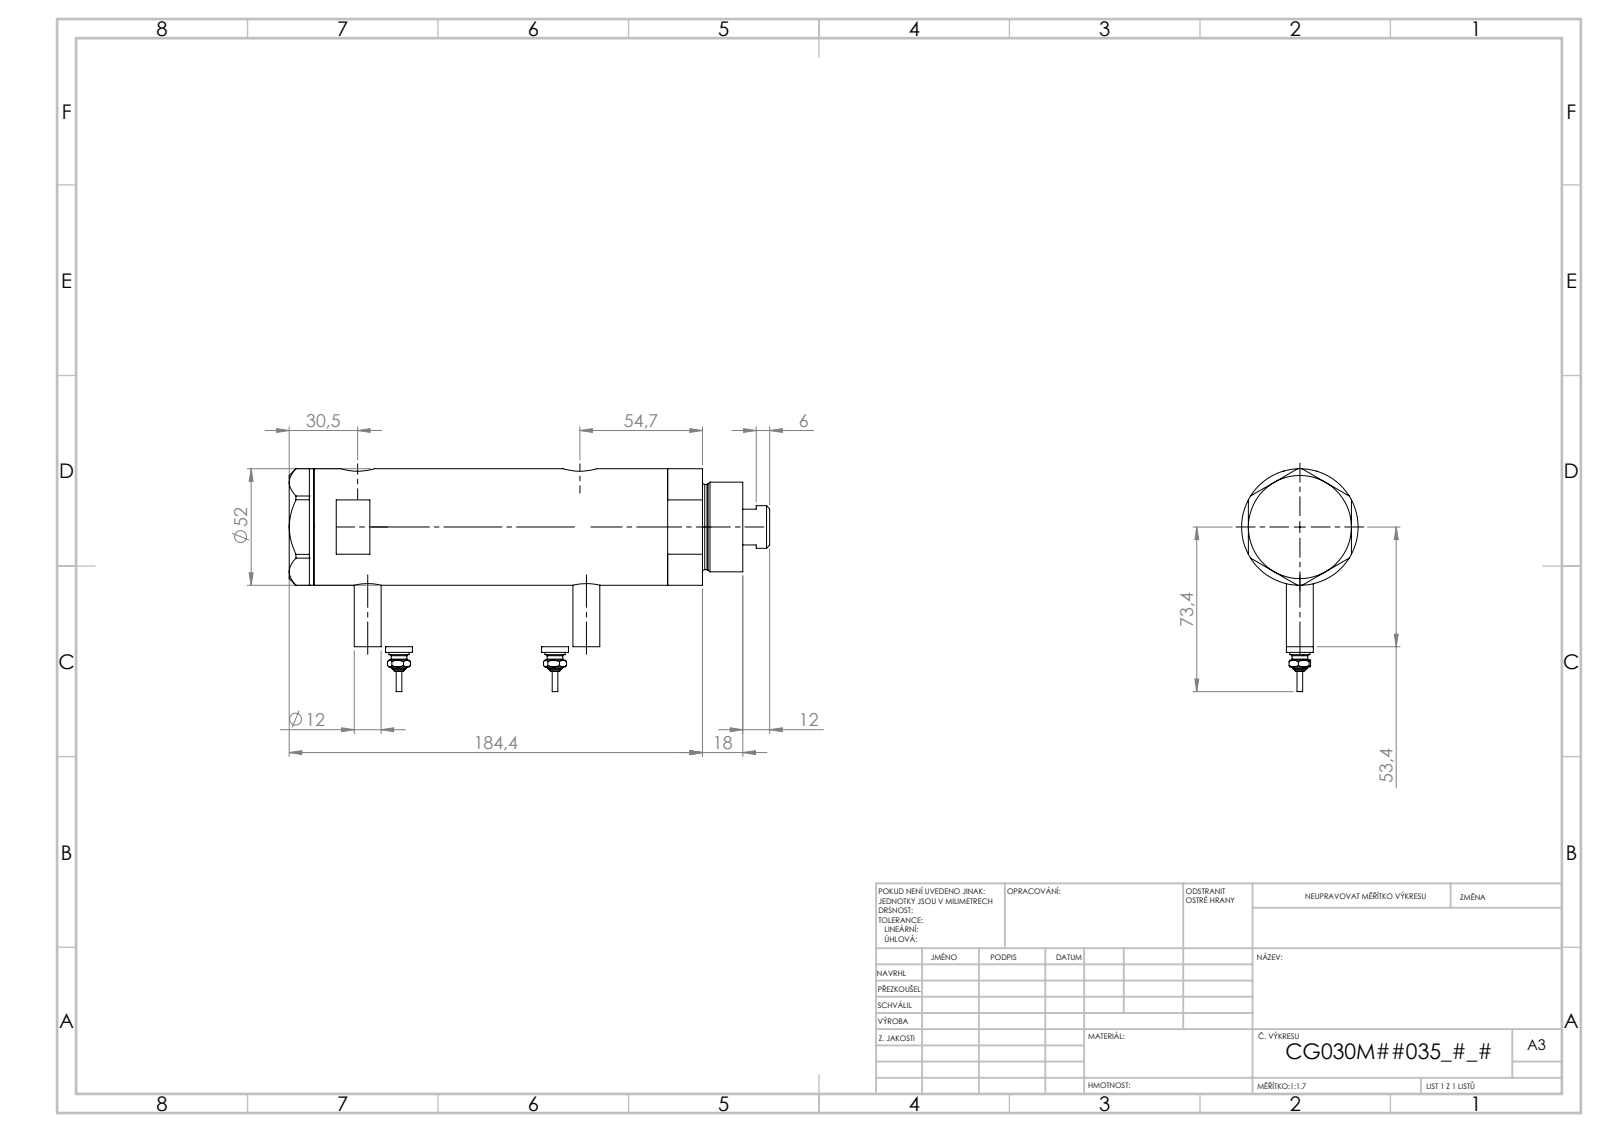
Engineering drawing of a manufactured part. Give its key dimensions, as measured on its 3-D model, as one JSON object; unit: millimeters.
{"part_name": "V270CG_VC; V270CG_SWITCH; V270CG_BACK; V270CG_MIDDLE (+1 more)", "step_written_by": "SolidWorks 2019 (CONFIG_CONTROL_DESIGN)", "units": "millimeters", "bodies": {"solids": 6, "faces": 246, "planar": 95, "cylindrical": 77, "other": 74}, "overall_size": [184.02, 84.3, 52], "volume_mm3": 330961, "surface_area_mm2": 78252, "round_holes": [[5, 2], [9.73, 2], [12.5, 2], [15, 2], [6.5, 1], [20, 1], [21.5, 1], [30, 1], [33, 1], [44, 1]], "round_bosses_or_shafts": [[12, 3], [9, 2], [7, 2], [4.34, 2], [2.4, 2], [52, 1], [40, 1], [38, 1]], "face_to_face_distances": [23.8, 11, 34.8, 46, 99.56, 88.56, 64.76, 135.96, 124.96, 101.16], "hole_center_spacings": [2.9, 4.5, 61.75, 64.65, 66.25, 69.15, 2.89, 2.91]}
